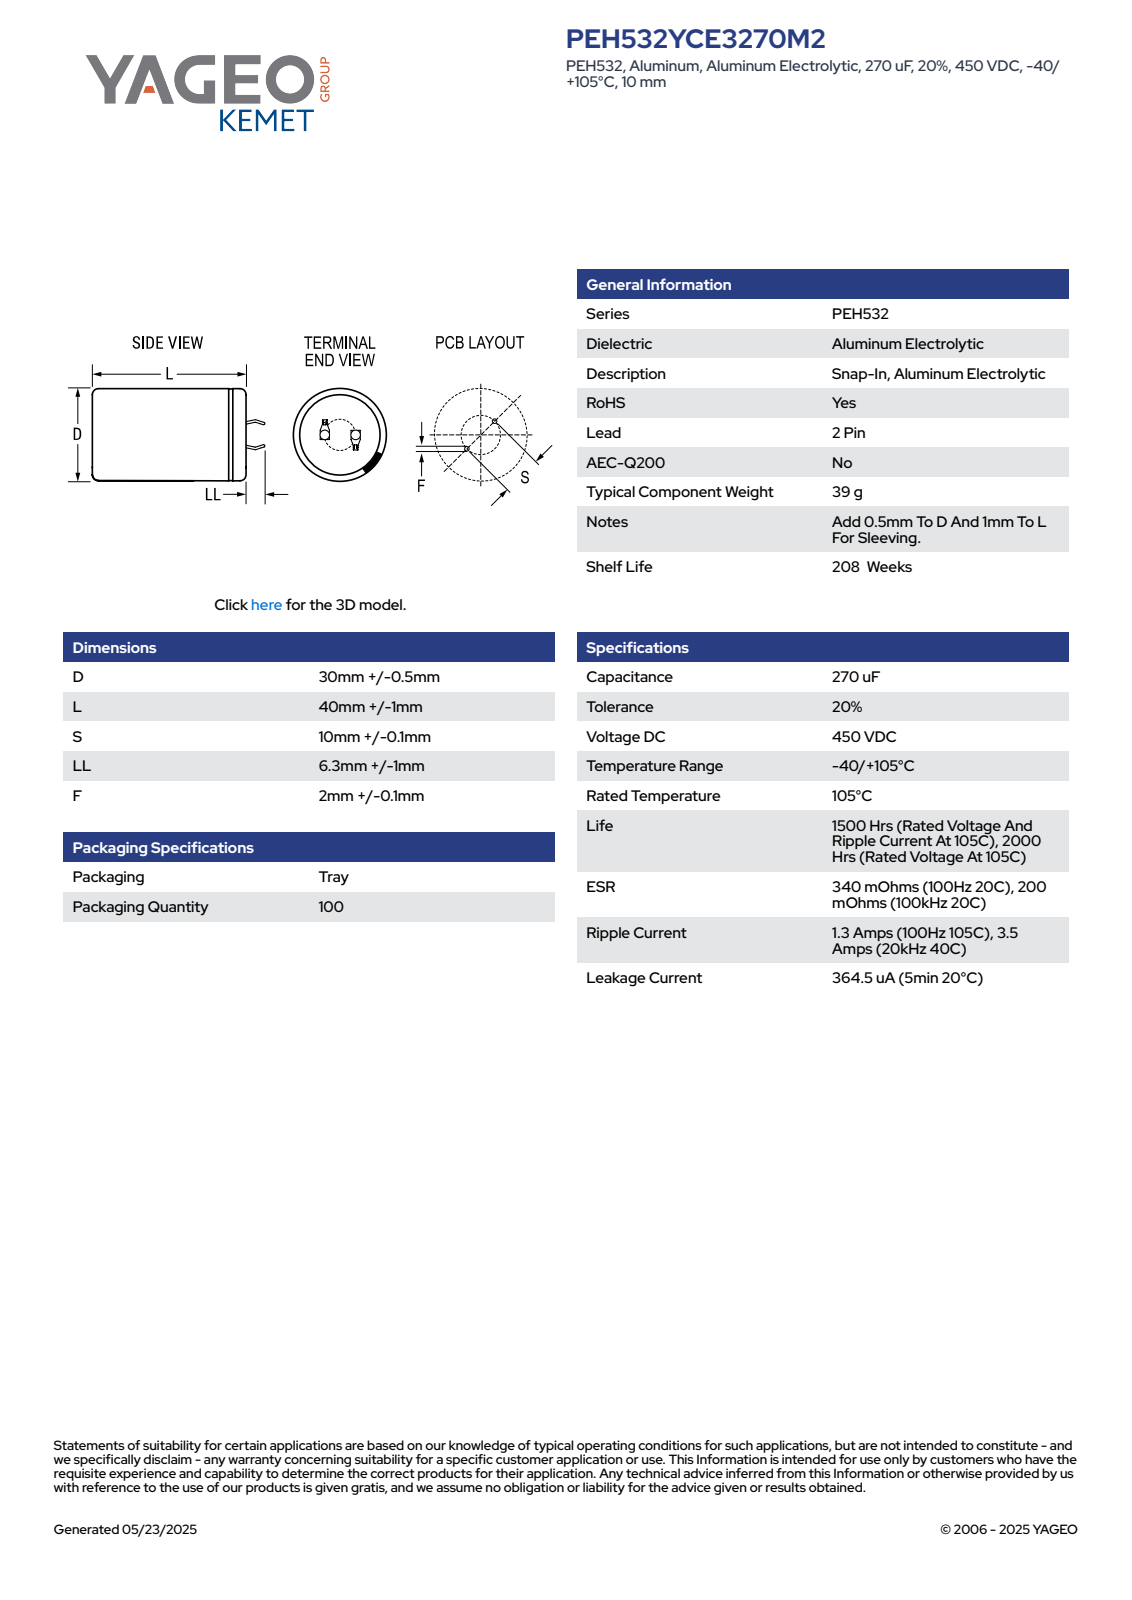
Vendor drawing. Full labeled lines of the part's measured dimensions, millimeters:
Part name (STEP PRODUCT): CARS_K2P_30X40_D30.5L41S10LL7.3F2.1
STEP written by: SolidWorks 2014 (AUTOMOTIVE_DESIGN)
Units: millimetres
Bodies: 1 solid, 100 faces (52 planar, 9 cylindrical, 39 other)
Overall size (bounding box): 48.29 × 30.5 × 30.5
Volume: 29 638 mm³ · Surface area: 5 401 mm²
Round holes (diameter × count): ⌀26.99 ×1
Round bosses / shafts (diameter × count): ⌀30.5 ×1
Partial cylindrical surfaces — rounded edges, fillets, slot ends (radius × count): R15.24 ×1
Main face-to-face distances: 40.99, 0.6, 41.49, 0.5, 7.08, 7.64, 0.75, 1.35, 7.68, 6.48
